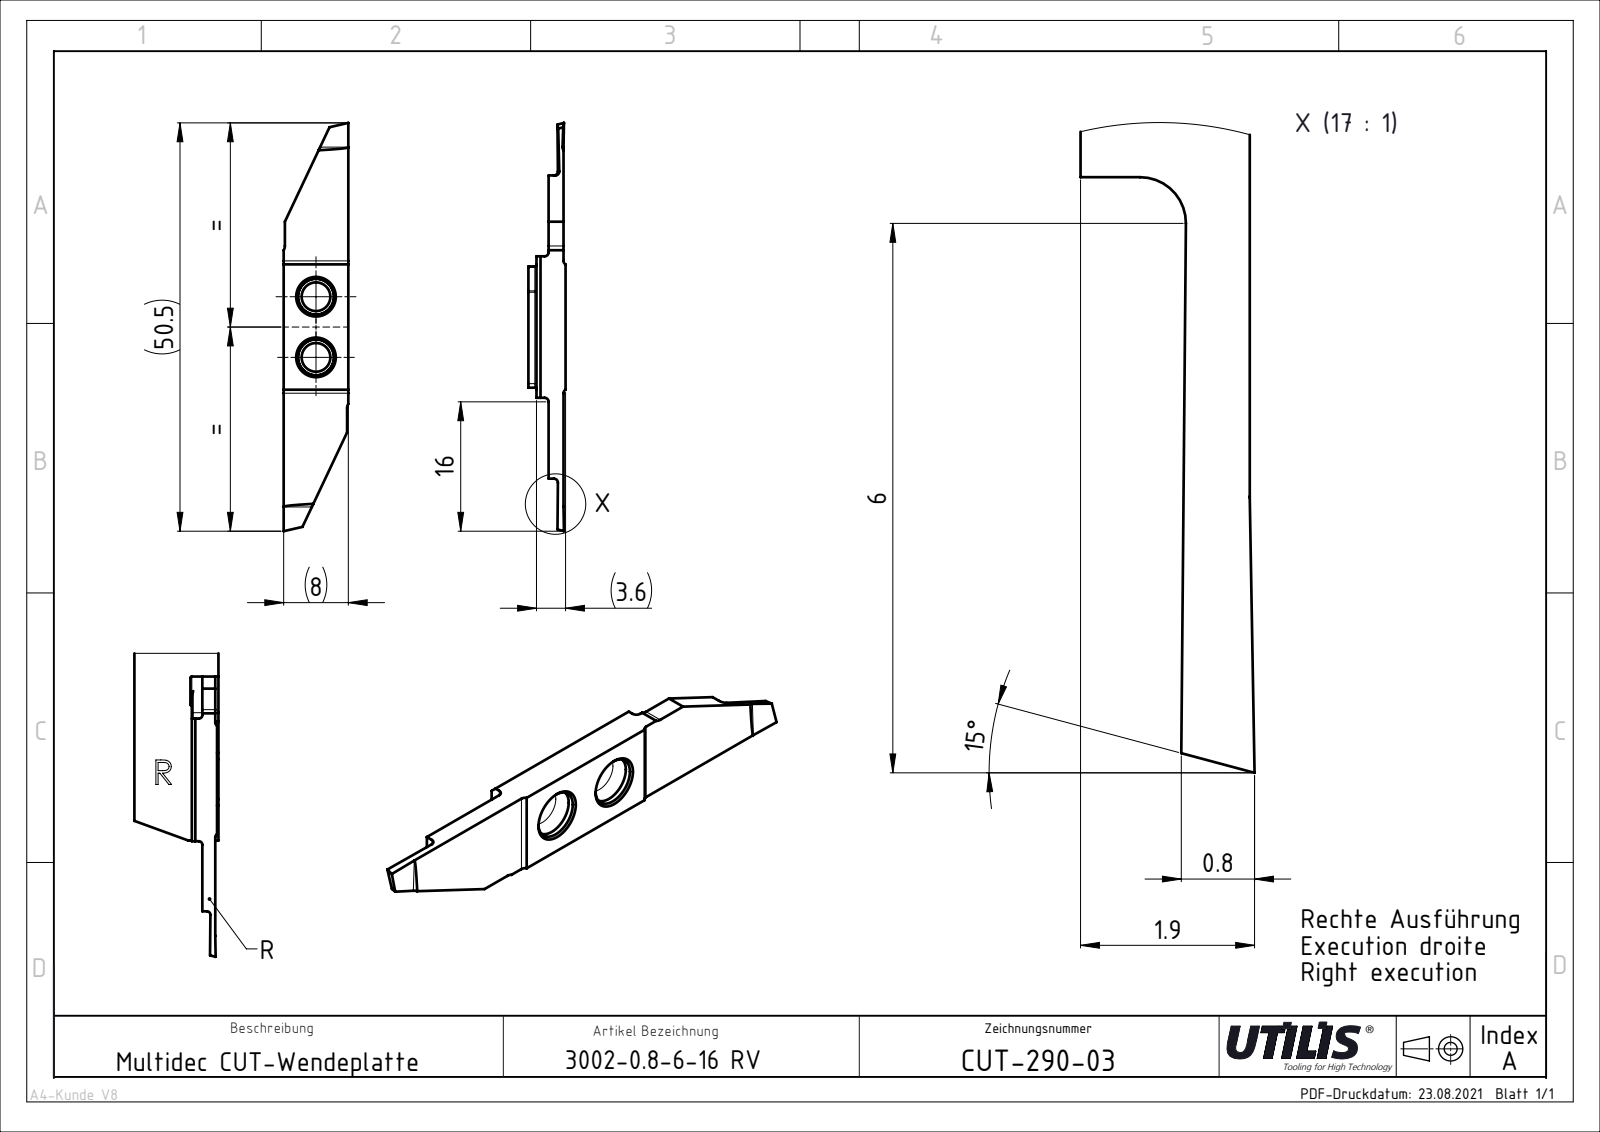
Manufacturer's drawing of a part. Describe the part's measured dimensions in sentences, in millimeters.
The part is named "CUT-290-03". Its 3-D file was written by "SolidWorks 2016 (AUTOMOTIVE_DESIGN)". It is 1 solid with 38 faces: 24 planar, 14 cylindrical and 0 other. Overall it measures 50.5 by 8 by 3.55 millimeters. Its volume is 719 cubic millimeters and its surface area 945 square millimeters. Round holes: 2 of diameter 3.55. Partial cylindrical surfaces (rounded edges, fillets, slot ends): 6 of radius 0.5, 2 of radius 0.15, 2 of radius 1. The main face-to-face distances are 1.85, 1.45, 3.3, 3.55, 2.1, 8, 18.1, 7.85, 17.5, 7.7. The hole center spacings are 7.5.
